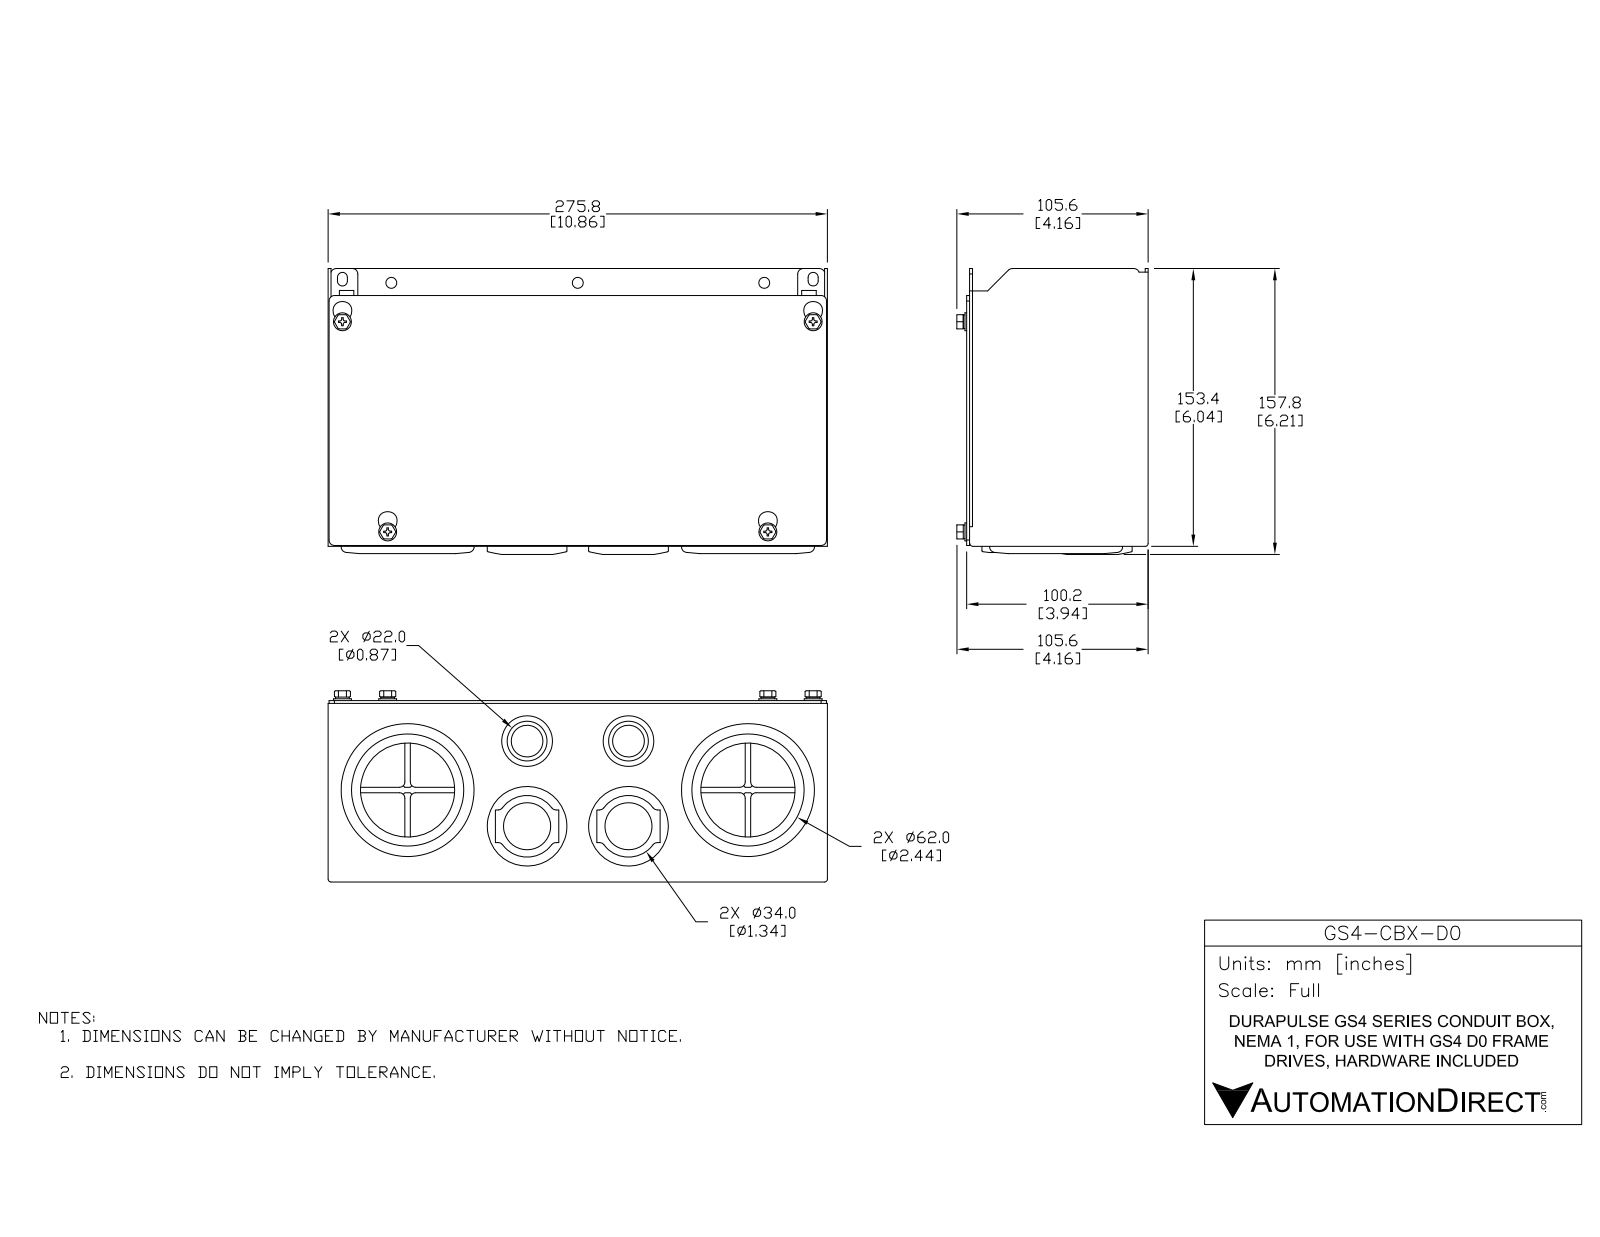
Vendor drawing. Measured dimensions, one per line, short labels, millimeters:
name: GS4-CBX-D0
written by: SolidWorks 2015 (AUTOMOTIVE_DESIGN)
unit: mm
bodies: 0 solids, 427 faces (157 planar, 165 cylindrical, 105 other)
size: 275.8 × 157.8 × 105.6
holes: 4× ⌀6.5, 4× ⌀10.5, 3× ⌀6, 2× ⌀17.5, 2× ⌀26, 2× ⌀52
bosses: 4× ⌀9.9, 4× ⌀7.5, 2× ⌀73.4, 2× ⌀44, 2× ⌀28, 2× ⌀8, 1× ⌀4.8
rounds: 20× R0.5, 20× R3, 16× R1, 6× R1.6, 4× R2.7, 2× R332.6, 1× R2, 1× R331.3
face distances: 1.6, 98.6, 97, 100.2, 274.2, 272.6, 275.8, 95.4, 3.2, 0.5
hole spacings: 6, 118.7, 262.1, 31.1, 34.5, 47, 56, 69
